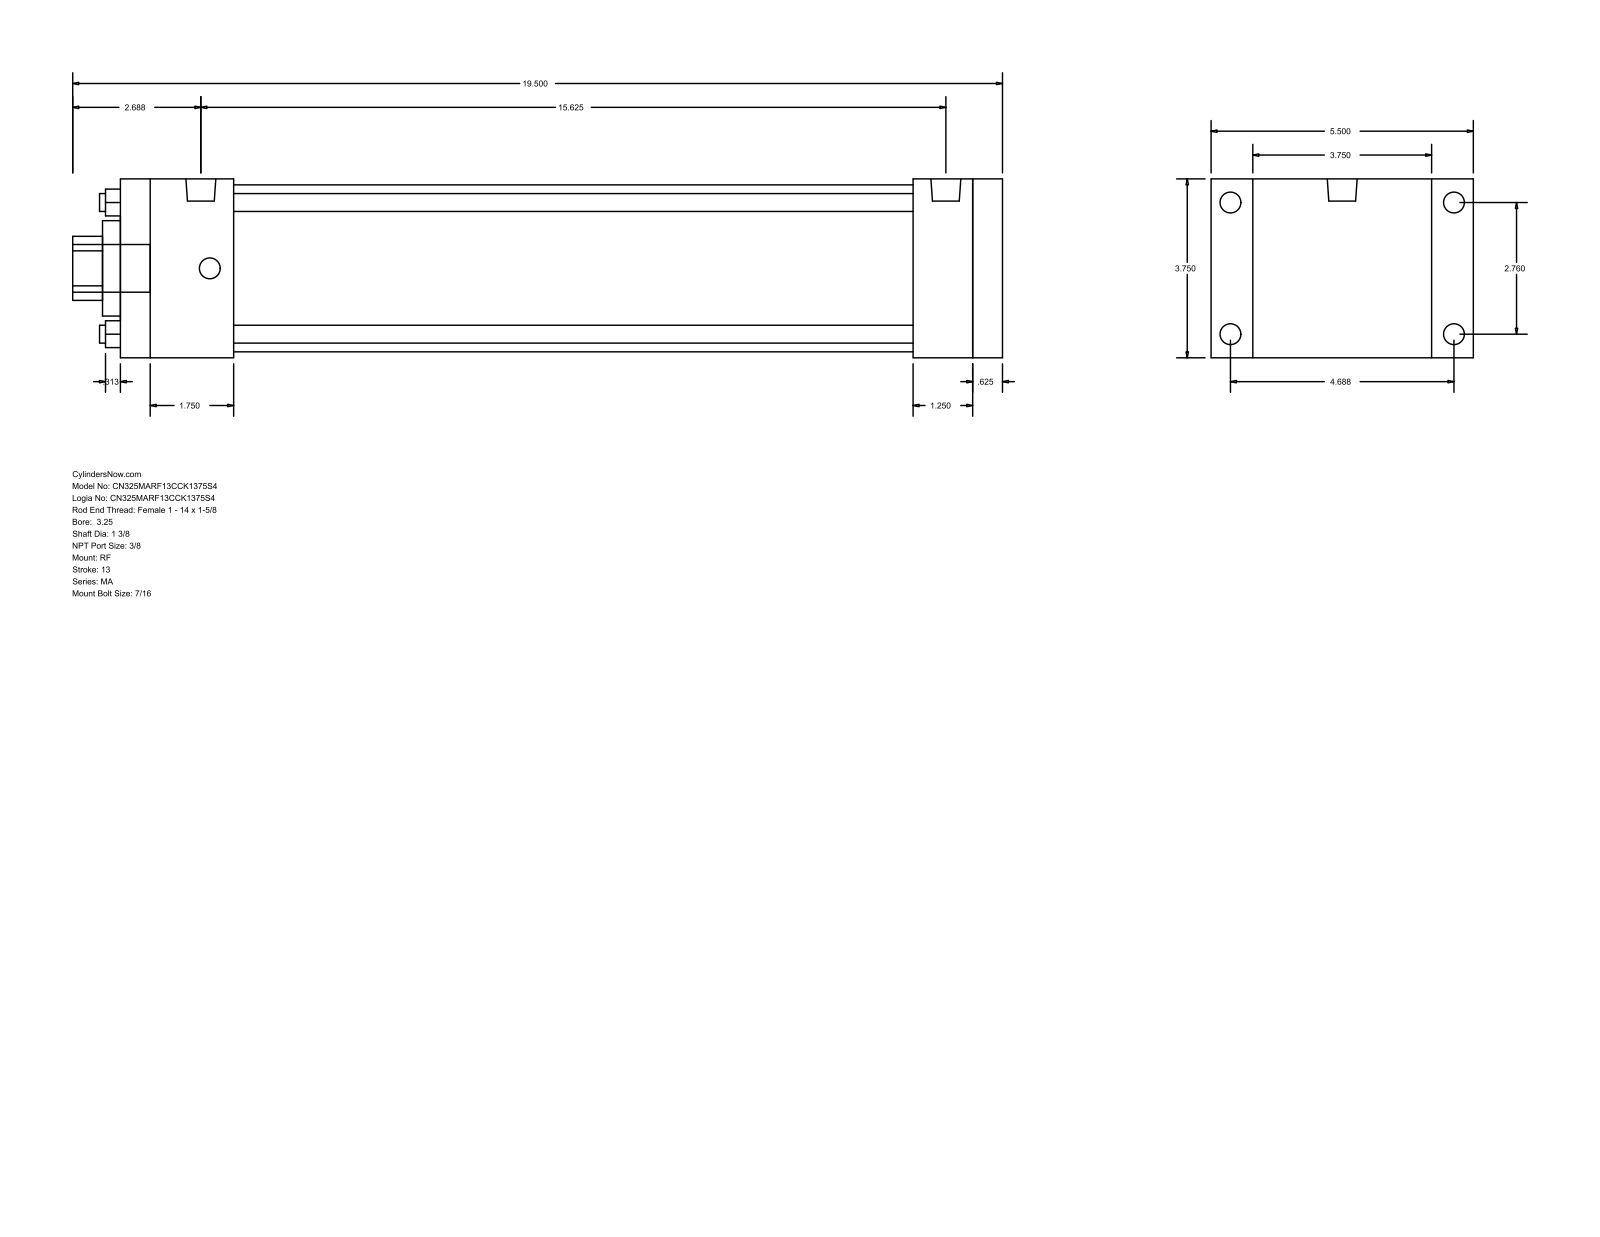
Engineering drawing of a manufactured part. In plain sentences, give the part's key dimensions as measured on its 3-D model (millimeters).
The part is named "MA_RF__0325_1.375". Its 3-D file was written by "GSSL Pune (CONFIG_CONTROL_DESIGN)". It is 0 solids with 92 faces: 64 planar, 28 cylindrical and 0 other. Overall it measures 495.3 by 139.7 by 95.25 millimeters. Round holes: 4 of diameter 9.53, 1 of diameter 34.92, 1 of diameter 50.8, 1 of diameter 88.9. Round bosses or shafts: 8 of diameter 11.11, 2 of diameter 15.93, 1 of diameter 25.4. Partial cylindrical surfaces (rounded edges, fillets, slot ends): 1 of radius 17.06. The main face-to-face distances are 95.24, 469.9, 15.87, 454.03, 22.23, 117.47, 422.28, 31.75, 47.62, 60.32. The hole center spacings are 49.57, 70.1, 99.14.
